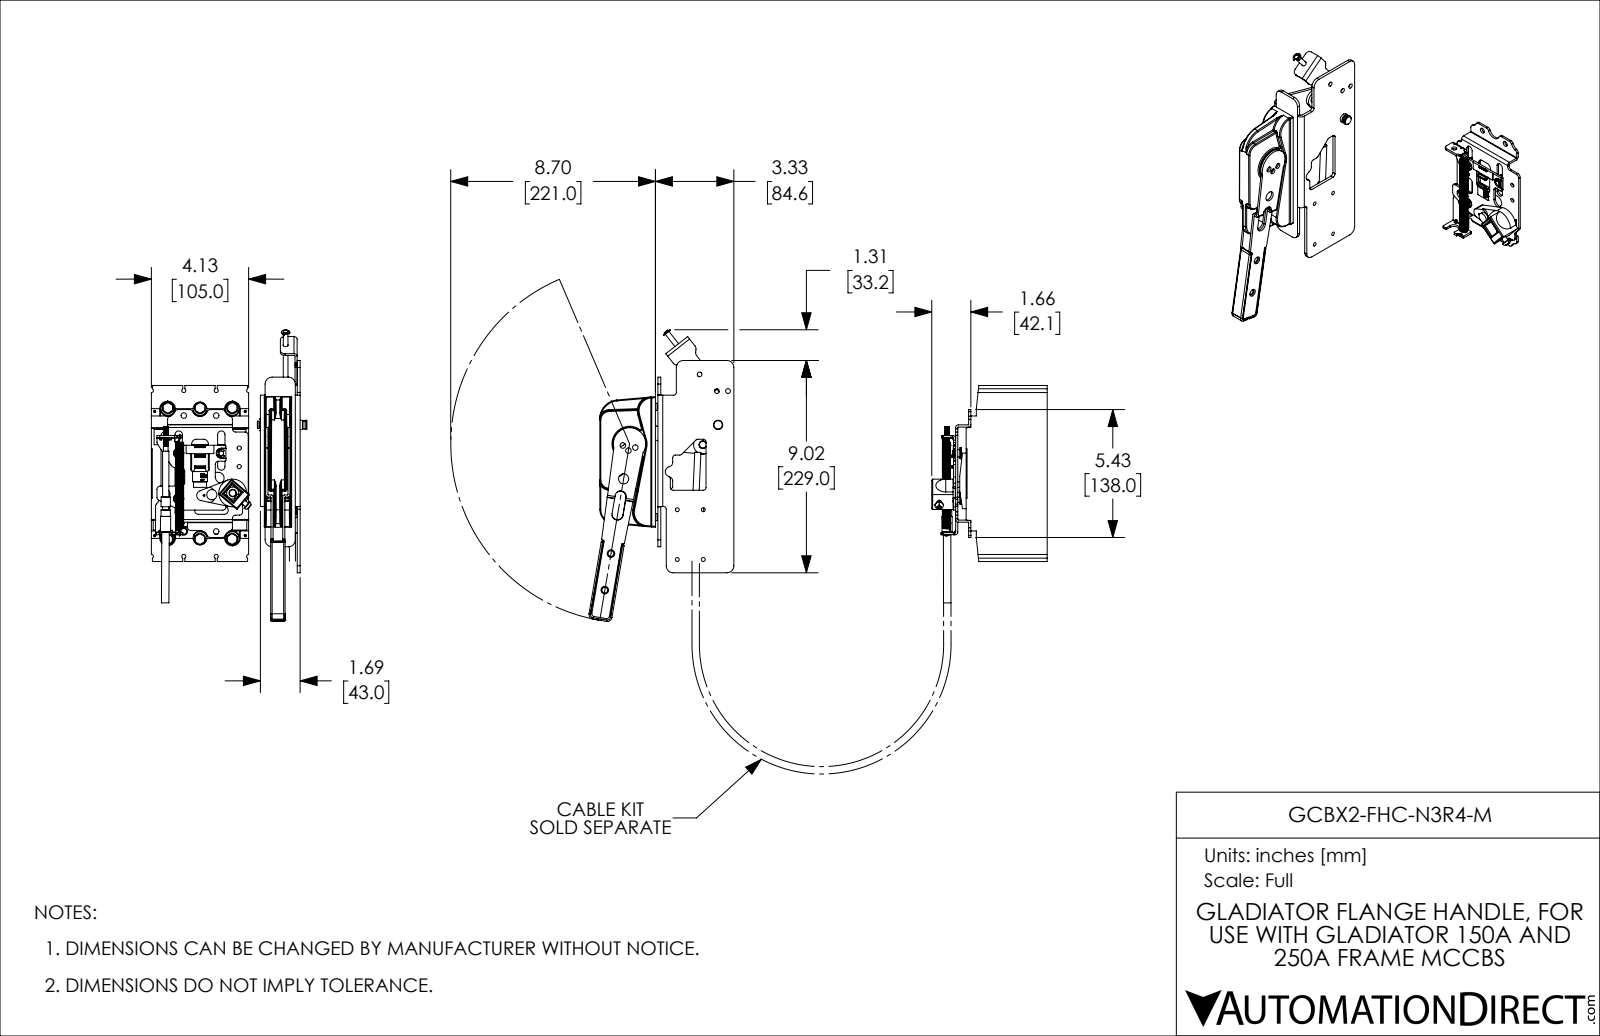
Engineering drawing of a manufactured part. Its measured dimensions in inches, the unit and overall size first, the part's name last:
Units: inches
Overall size (bounding box): 19.475 × 12.394 × 6.611
Round holes (diameter × count): ⌀0.157 ×25, ⌀0.067 ×24, ⌀0.098 ×10, ⌀0.236 ×6, ⌀0.244 ×6, ⌀0.354 ×6, ⌀0.591 ×6, ⌀0.689 ×6, ⌀0.165 ×4, ⌀0.173 ×4, ⌀0.201 ×4, ⌀0.205 ×4
Round bosses / shafts (diameter × count): ⌀0.197 ×8, ⌀0.709 ×6, ⌀0.394 ×5, ⌀0.157 ×5, ⌀0.315 ×4, ⌀0.472 ×3, ⌀0.433 ×3, ⌀0.307 ×3
Partial cylindrical surfaces — rounded edges, fillets, slot ends (radius × count): R0.012 ×210, R0.039 ×150, R0.02 ×65, R0.059 ×48, R0.079 ×42, R0.118 ×35, R0.138 ×34, R0.009 ×30
Main face-to-face distances: 0.126, 0.091, 4.134, 2.064, 2.19, 6.198, 6.324, 1.368, 0.22, 0.72
Hole centre spacings: 1.378, 5.24, 0.743, 1.046, 6.298, 5.982, 0.56, 1.065
Volume: 104.2 in³ · Surface area: 618.6 in²
Bodies: 40 solids, 4794 faces (2462 planar, 1758 cylindrical, 574 other)
Part name (STEP PRODUCT): GCBX2-FHC-N3R4-M; GCB250S-3FF250LL; GCBX2-CBL-36_2; GCBX2-FHC-N3R4-M_2 (+1 more)
STEP written by: SolidWorks 2021 (CONFIG_CONTROL_DESIGN)
